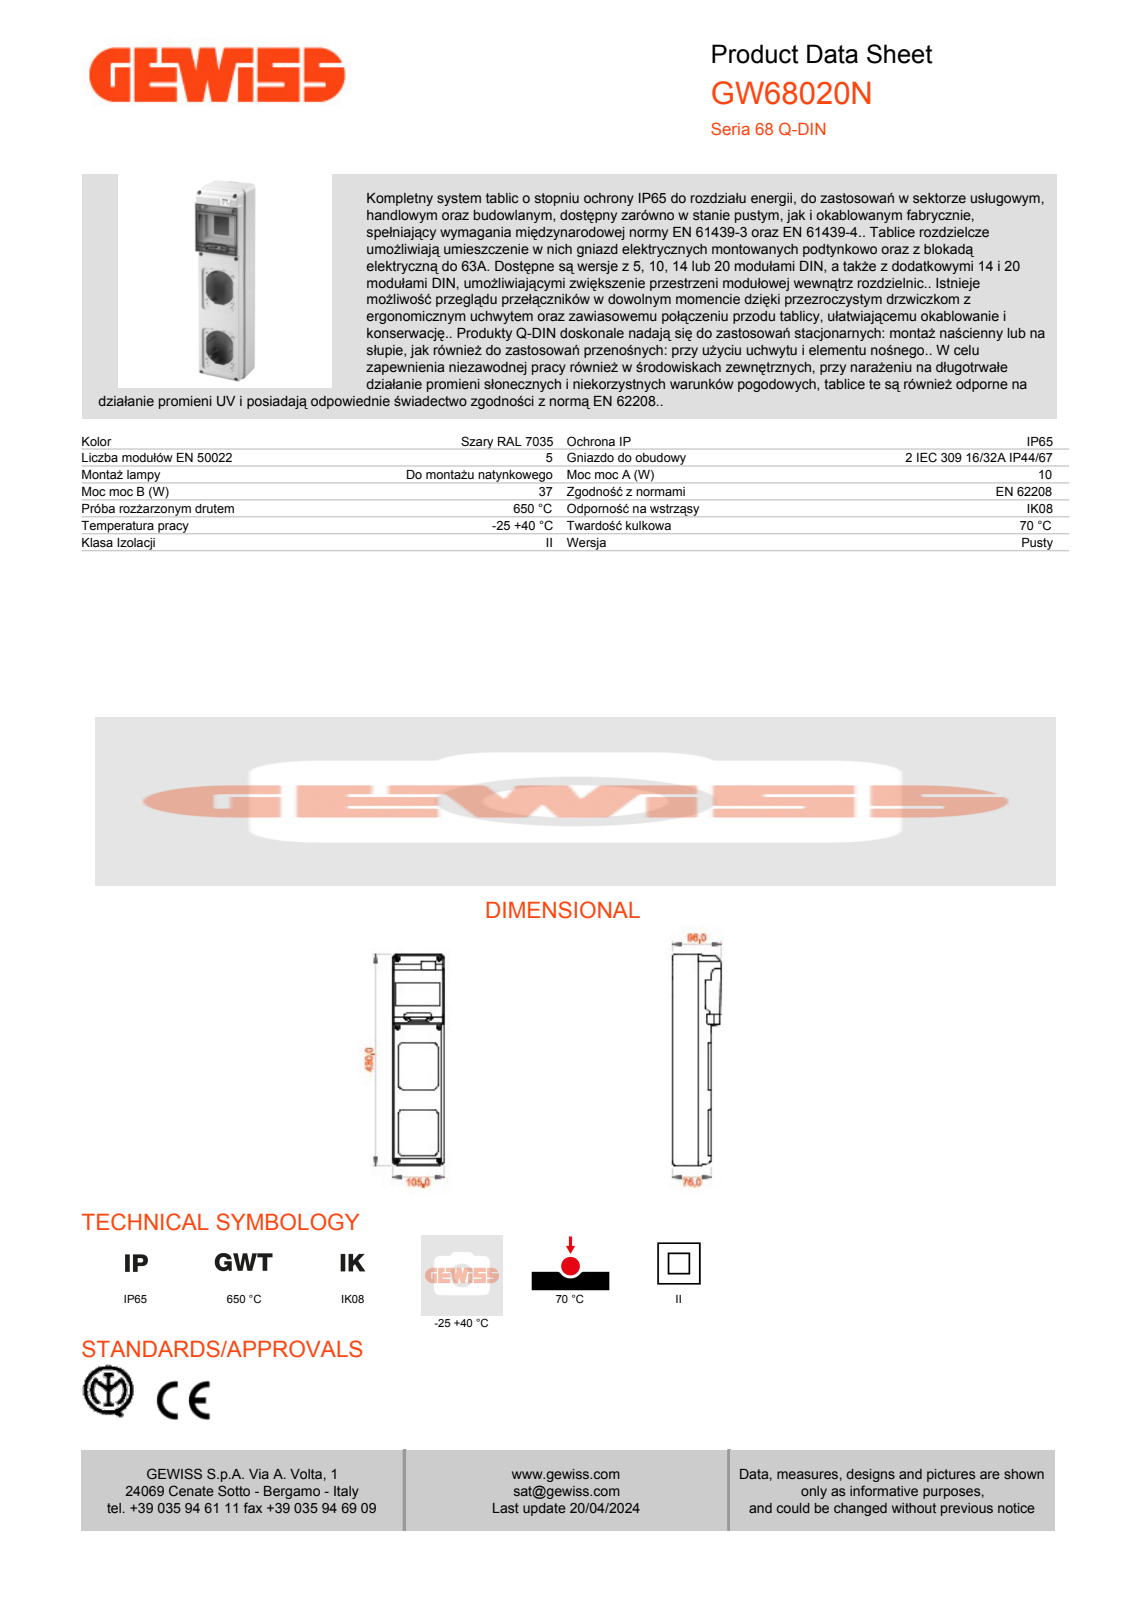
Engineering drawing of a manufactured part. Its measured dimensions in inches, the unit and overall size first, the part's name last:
Units: inches
Overall size (bounding box): 16.929 × 4.134 × 3.939
Partial cylindrical surfaces — rounded edges, fillets, slot ends (radius × count): R0.02 ×8, R0.039 ×8, R0.059 ×8, R0.394 ×6, R0.079 ×5, R0.051 ×4, R0.098 ×4, R0.118 ×4
Main face-to-face distances: 0.098, 3.822, 0.088, 4.134, 3.911, 0.413, 3.189, 3.287, 3.701, 3.602
Volume: 46.07 in³ · Surface area: 584.5 in²
Bodies: 2 solids, 711 faces (454 planar, 65 cylindrical, 192 other)
Part name (STEP PRODUCT): 55523971_FONDO_QDIN_5M_3PR_16A; 55524300E; GW68020N_ASM
STEP written by: CREO PARAMETRIC BY PTC INC, 2020354 (CONFIG_CONTROL_DESIGN)
